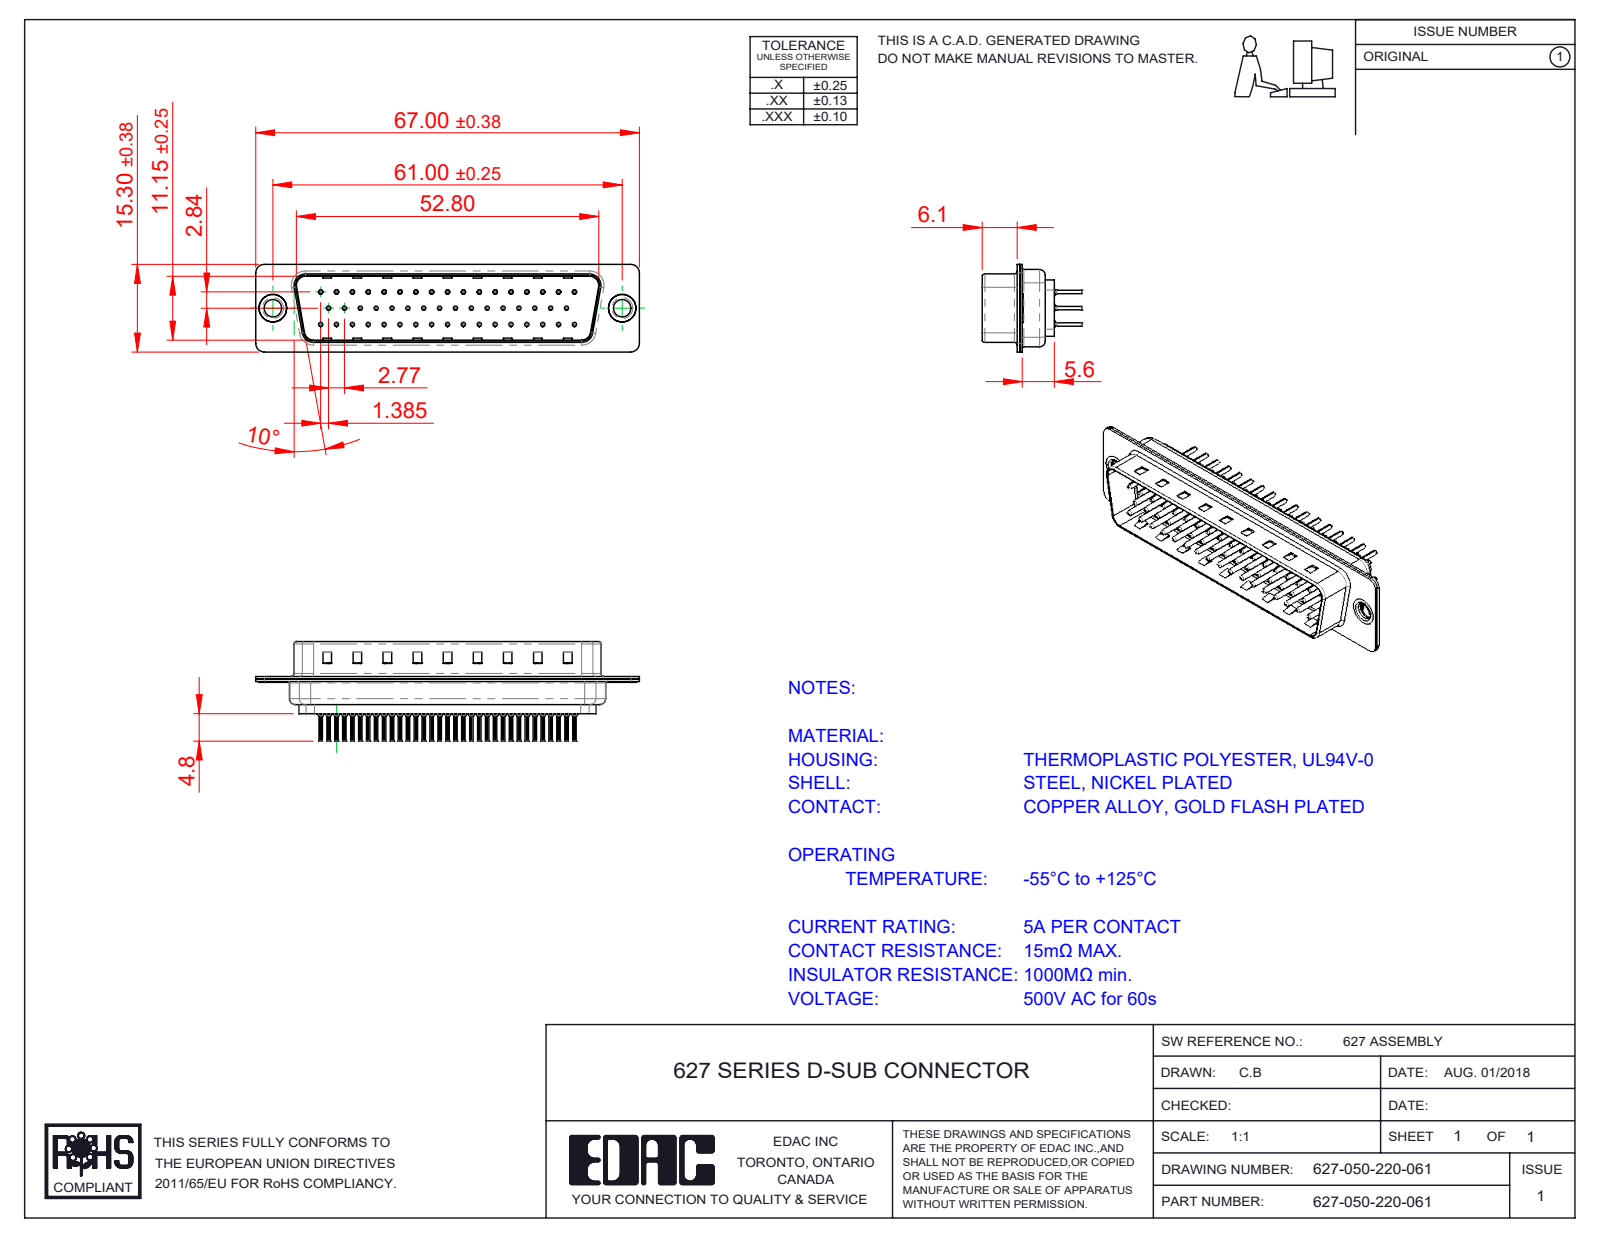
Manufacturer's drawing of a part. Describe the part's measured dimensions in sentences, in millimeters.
The part is named "627 Contact Row 3_20L; 627 Shell Front_50 Contacts; 627-050-220-061; 627 Contact Row 2_20L (+4 more)". Its 3-D file was written by "SolidWorks 2020 (CONFIG_CONTROL_DESIGN)". It is 55 solids with 5286 faces: 1403 planar, 1975 cylindrical and 1908 other. Overall it measures 67 by 17.3 by 15.3 millimeters. Its volume is 4 346 cubic millimeters and its surface area 12 440 square millimeters. Round holes: 50 of diameter 0.2, 50 of diameter 0.35, 50 of diameter 1.1, 50 of diameter 1.6, 2 of diameter 3.05, 2 of diameter 4, 2 of diameter 4.8. Round bosses or shafts: 50 of diameter 2, 50 of diameter 1.5, 50 of diameter 0.75, 50 of diameter 0.6, 2 of diameter 5, 2 of diameter 4.9, 2 of diameter 3.55. Partial cylindrical surfaces (rounded edges, fillets, slot ends): 100 of radius 0.1, 16 of radius 1.5, 12 of radius 2, 8 of radius 0.5, 8 of radius 1.6, 4 of radius 0.25, 4 of radius 0.6, 4 of radius 0.65. The main face-to-face distances are 0.4, 0.45, 11.55, 0.9, 6.05, 6.5, 0.78, 12.33, 1.95, 0.77. The hole center spacings are 3.16, 2.77, 5.54, 8.31, 11.08, 13.85, 16.62, 5.03.
